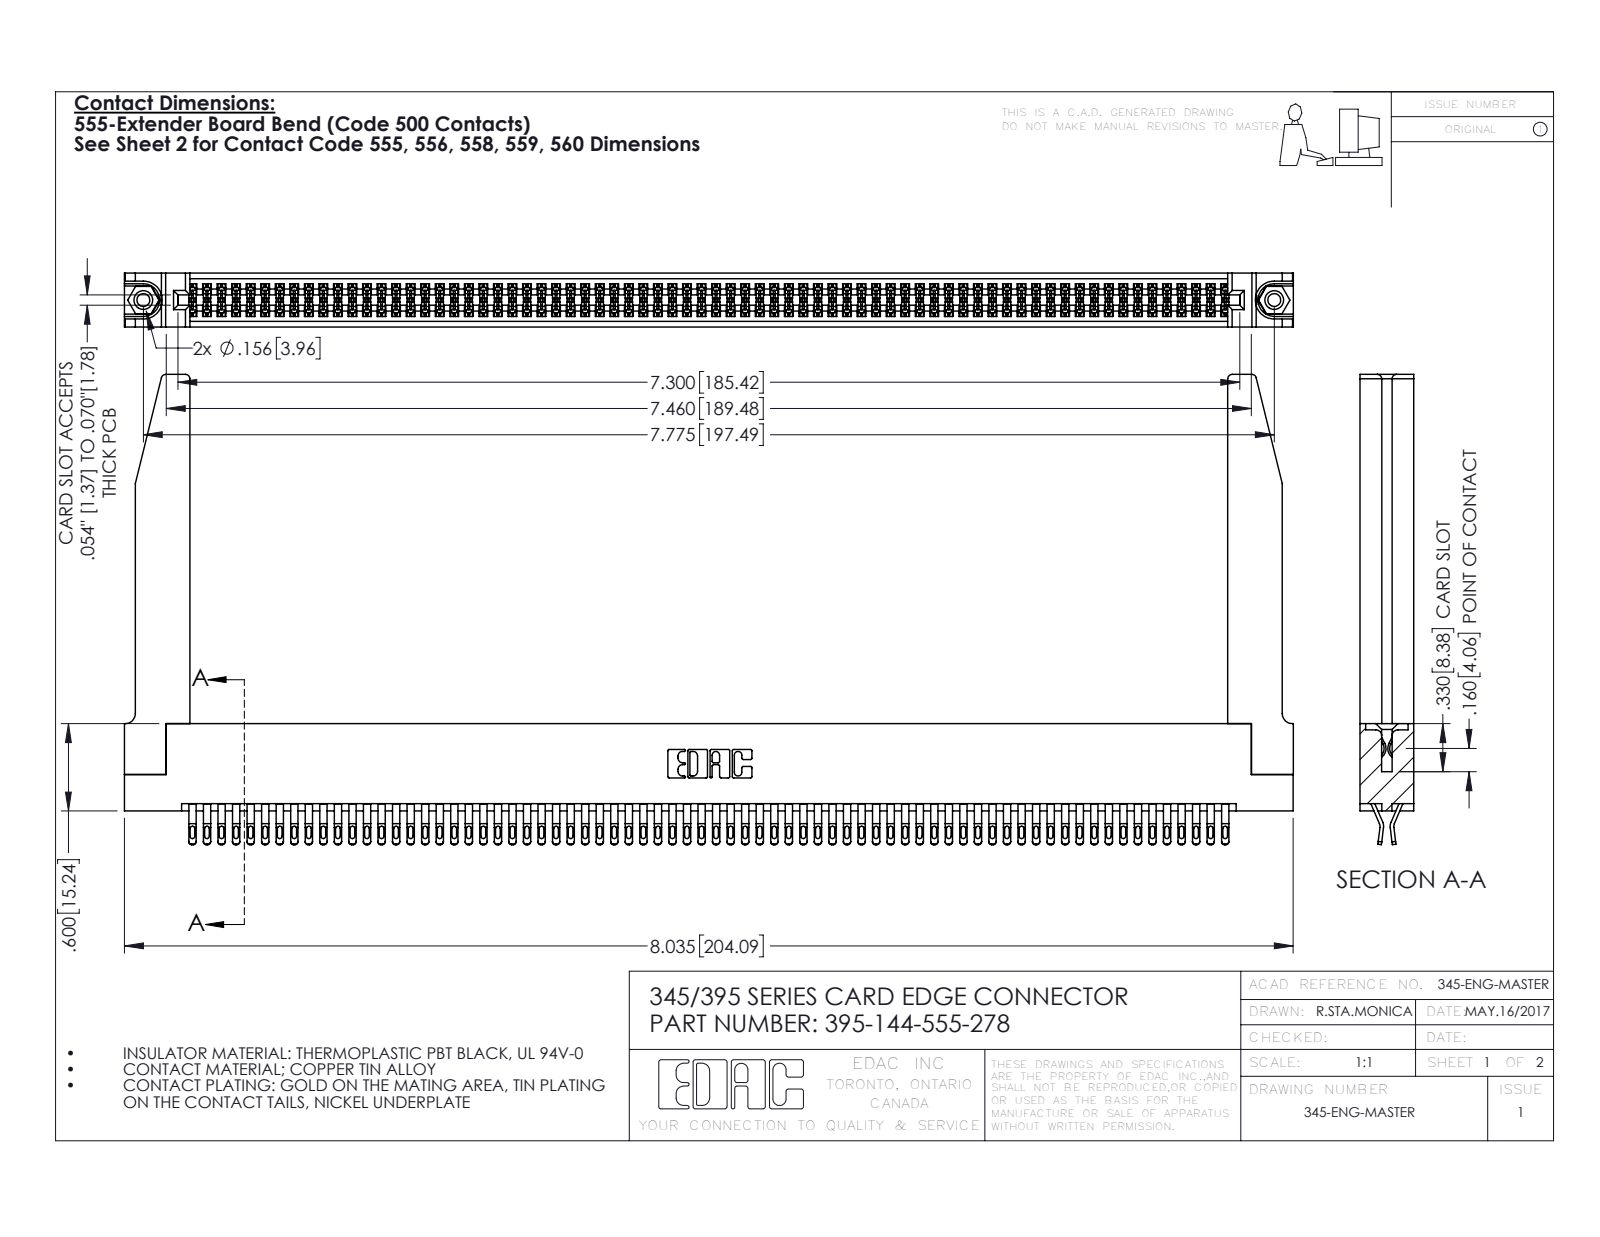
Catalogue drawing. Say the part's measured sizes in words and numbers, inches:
The part is named "345 Part_Flush Mounting Lugs - 0.156 Dia-TH; 395-144-555-278; 345-250-001_345-250-001-102; 345-292-001_555 Tail (+1 more)". Its 3-D file was written by "SolidWorks 2016 (CONFIG_CONTROL_DESIGN)". It is 149 solids with 8424 faces: 4686 planar, 3686 cylindrical and 52 other. Overall it measures 8.036 by 3.232 by 0.37 inches. Its volume is 1.727 cubic inches and its surface area 60.78 square inches. Round holes: 2 of diameter 0.089, 2 of diameter 0.125, 2 of diameter 0.156, 1 of diameter 0.064. Round bosses or shafts: 2 of diameter 0.155. Partial cylindrical surfaces (rounded edges, fillets, slot ends): 360 of radius 0.016, 288 of radius 0.02, 216 of radius 0.006, 22 of radius 0.01, 8 of radius 0.03, 6 of radius 0.007, 6 of radius 0.031, 3 of radius 0.026. The main face-to-face distances are 0.072, 0.298, 0.37, 0.025, 0.2, 0.098, 0.272, 0.225, 0.175, 0.149. The hole center spacings are 0.27, 7.539, 7.775.
